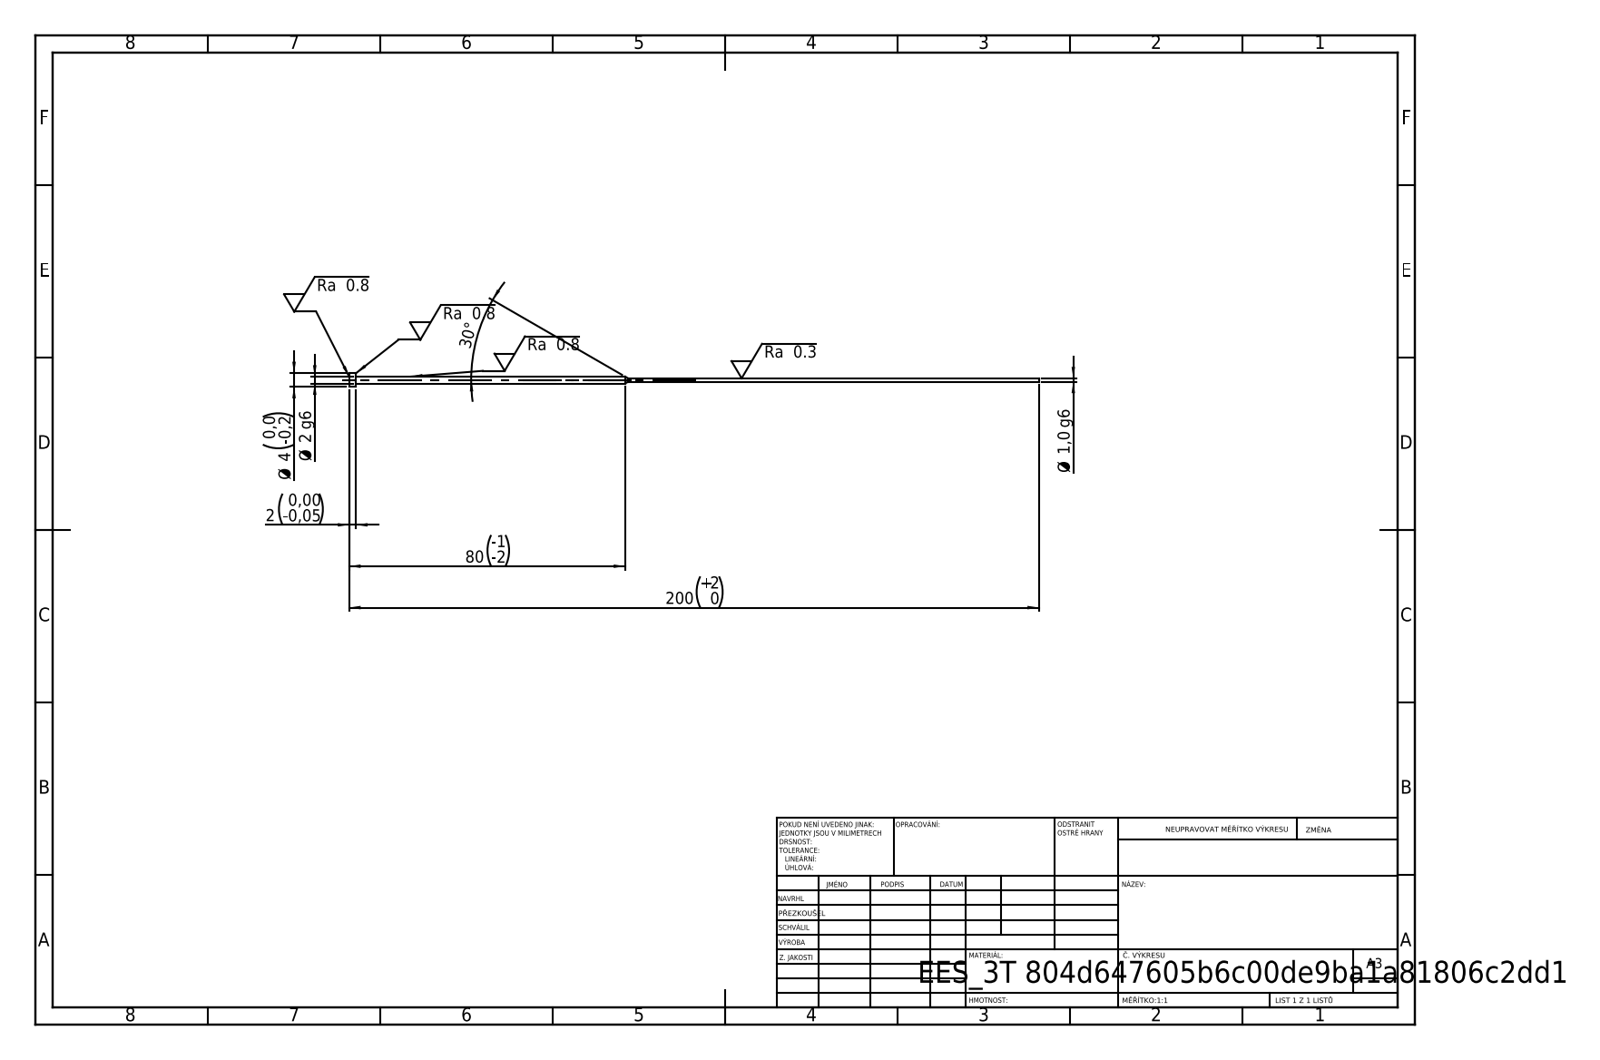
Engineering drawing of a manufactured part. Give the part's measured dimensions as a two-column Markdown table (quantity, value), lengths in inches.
| quantity | value |
| --- | --- |
| STEP written by | SolidWorks 2019 (CONFIG_CONTROL_DESIGN) |
| units | inches |
| bodies | 1 solid, 11 faces (3 planar, 6 cylindrical, 2 other) |
| overall size | 7.874 × 0.157 × 0.157 |
| volume | 0.022 in³ |
| surface area | 1.42 in² |
| round bosses / shafts (diameter × count) | 0.157 × 1, 0.079 × 1, 0.039 × 1 |
| main face-to-face distances | 0.079, 7.795, 7.874 |
